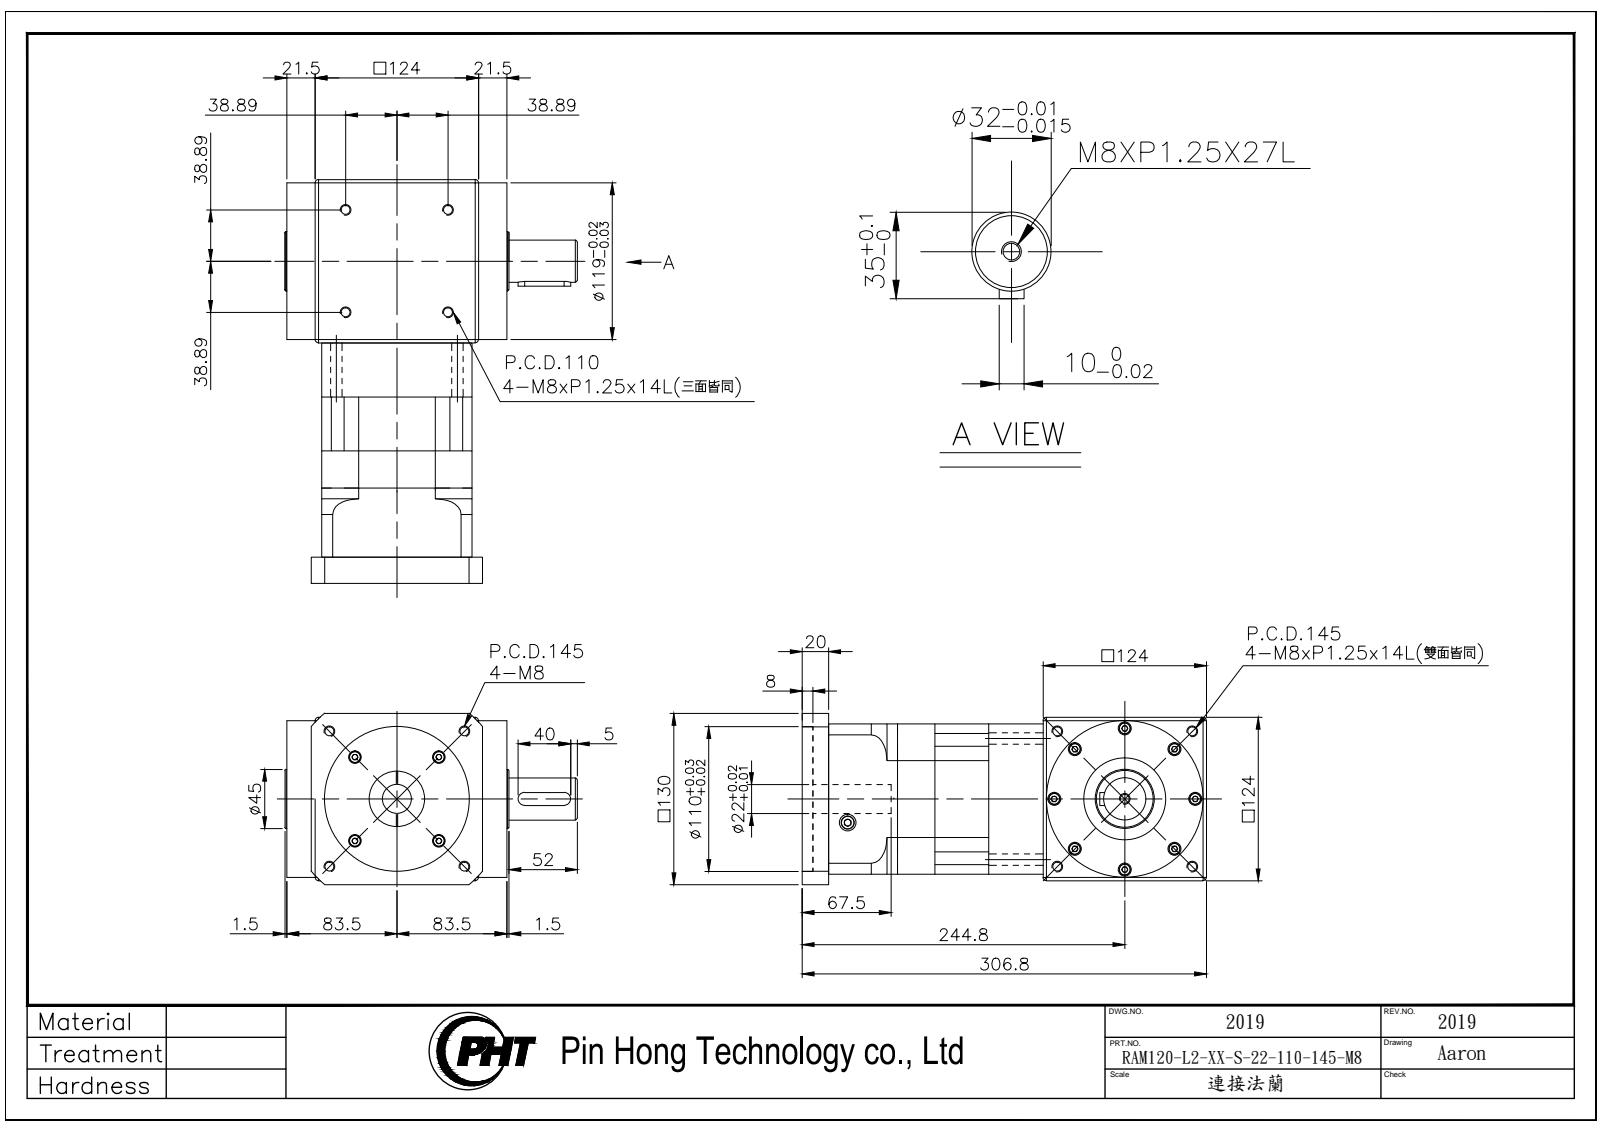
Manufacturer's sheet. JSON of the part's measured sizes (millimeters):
{"part_name": "RAM120-L2-XX-S-22-110-145-M8_2019", "step_written_by": "SolidWorks 2016 (AUTOMOTIVE_DESIGN)", "units": "millimeters", "bodies": {"solids": 6, "faces": 883, "planar": 418, "cylindrical": 305, "other": 160}, "overall_size": [306.8, 222, 130], "volume_mm3": 4542000, "surface_area_mm2": 380358, "round_holes": [[6.8, 17], [9.5, 12], [5.3, 8], [9, 8], [14, 8], [4.2, 4], [5.5, 4], [8.6, 4], [12.7, 2], [4.08, 1], [22, 1], [42, 1]], "round_bosses_or_shafts": [[13, 12], [8.5, 4], [119, 1], [62, 1], [49, 1], [45, 1], [32, 1]], "partial_cylinders_radius": [[7, 4], [5, 2], [64, 1], [75, 1], [85, 1], [86.2, 1]], "face_to_face_distances": [5, 119, 124, 114, 69.5, 28.3, 41.2, 3, 41, 110.5], "hole_center_spacings": [59, 10, 15.4, 17.24, 19.42, 21.77, 39.8, 51.28]}
